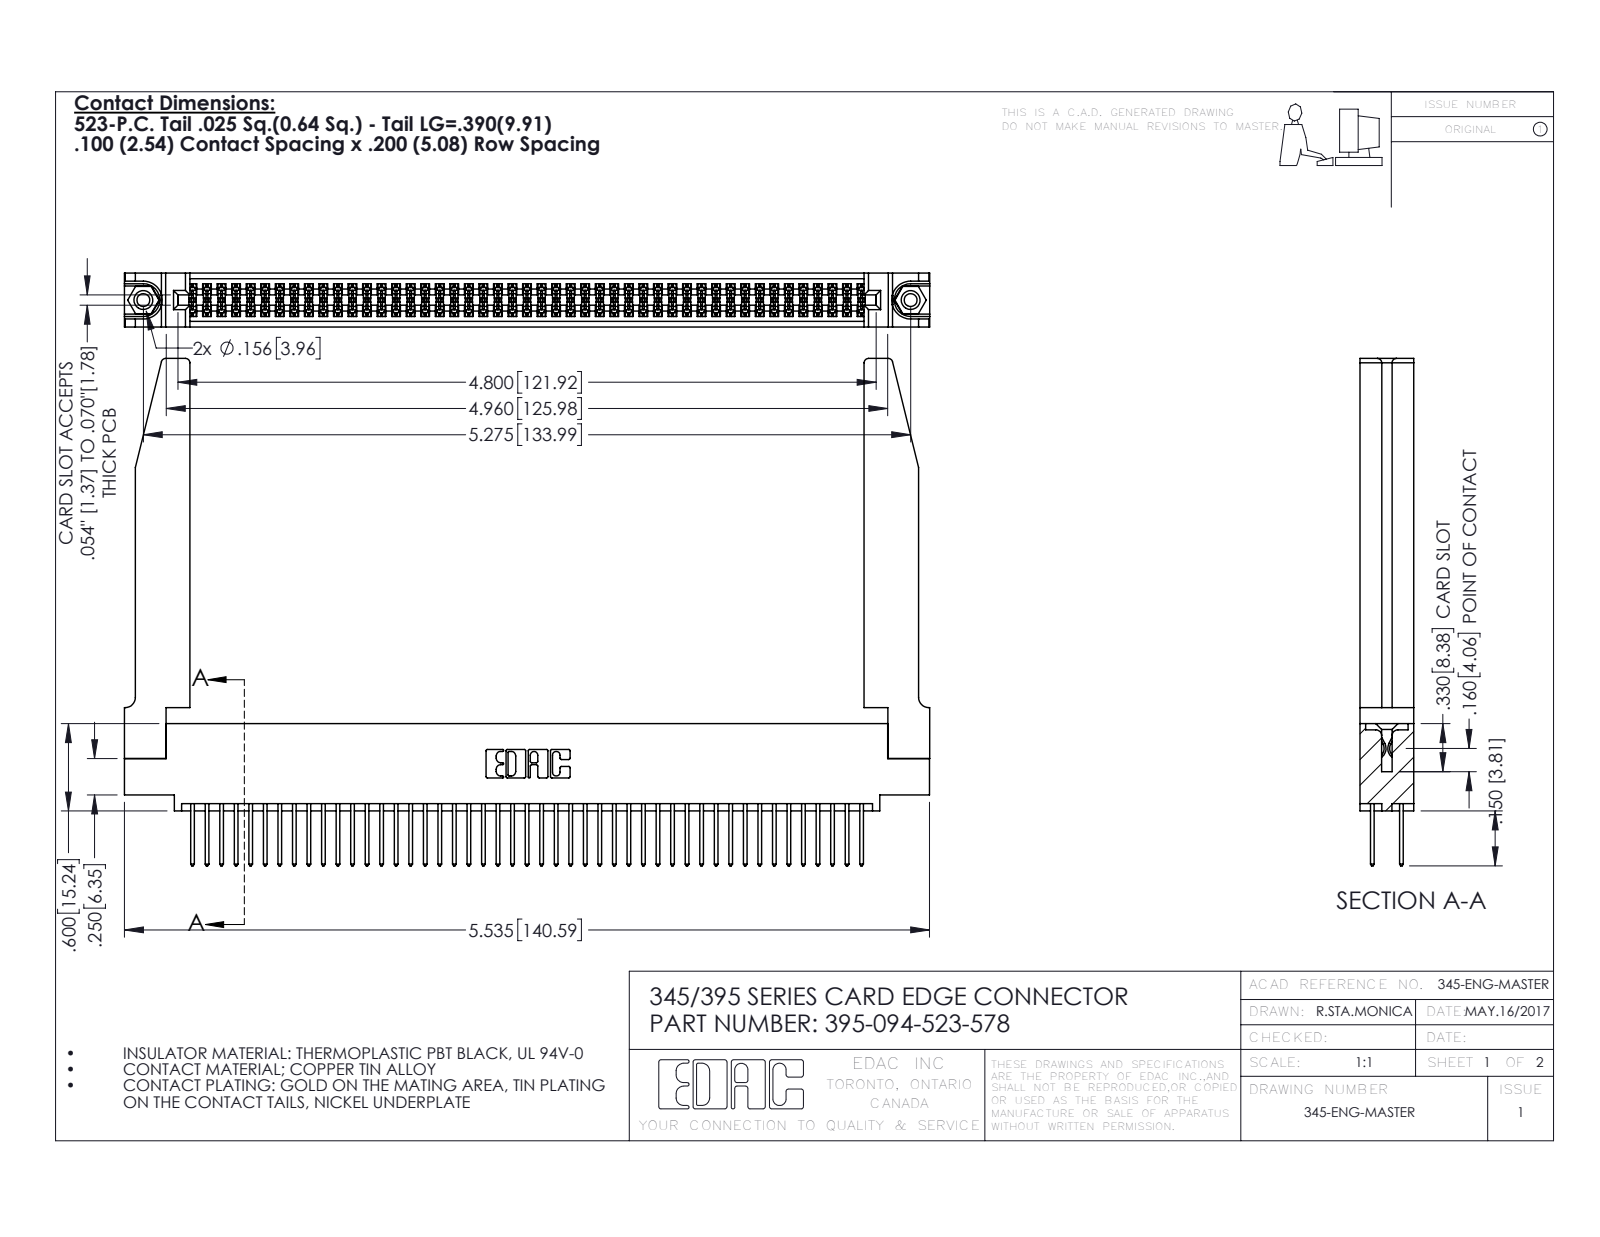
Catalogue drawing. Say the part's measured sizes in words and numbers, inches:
The part is named "345-250-001_345-250-001-102; 345-220-078_345-220-078; 345-292-001_345-293-123; 345 Part_0.110 Offset - 0.156 Dia-TH (+1 more)". Its 3-D file was written by "SolidWorks 2016 (CONFIG_CONTROL_DESIGN)". It is 99 solids with 5064 faces: 3328 planar, 1684 cylindrical and 52 other. Overall it measures 5.536 by 3.487 by 0.37 inches. Its volume is 1.318 cubic inches and its surface area 43.91 square inches. Round holes: 2 of diameter 0.089, 2 of diameter 0.125, 2 of diameter 0.156, 1 of diameter 0.064. Round bosses or shafts: 2 of diameter 0.155. Partial cylindrical surfaces (rounded edges, fillets, slot ends): 141 of radius 0.006, 94 of radius 0.01, 22 of radius 0.01, 8 of radius 0.03, 6 of radius 0.007, 6 of radius 0.031, 3 of radius 0.026, 2 of radius 0.014. The main face-to-face distances are 0.072, 0.298, 0.37, 0.098, 0.272, 0.025, 0.2, 0.225, 0.175, 0.148. The hole center spacings are 0.27, 5.039, 5.275.
